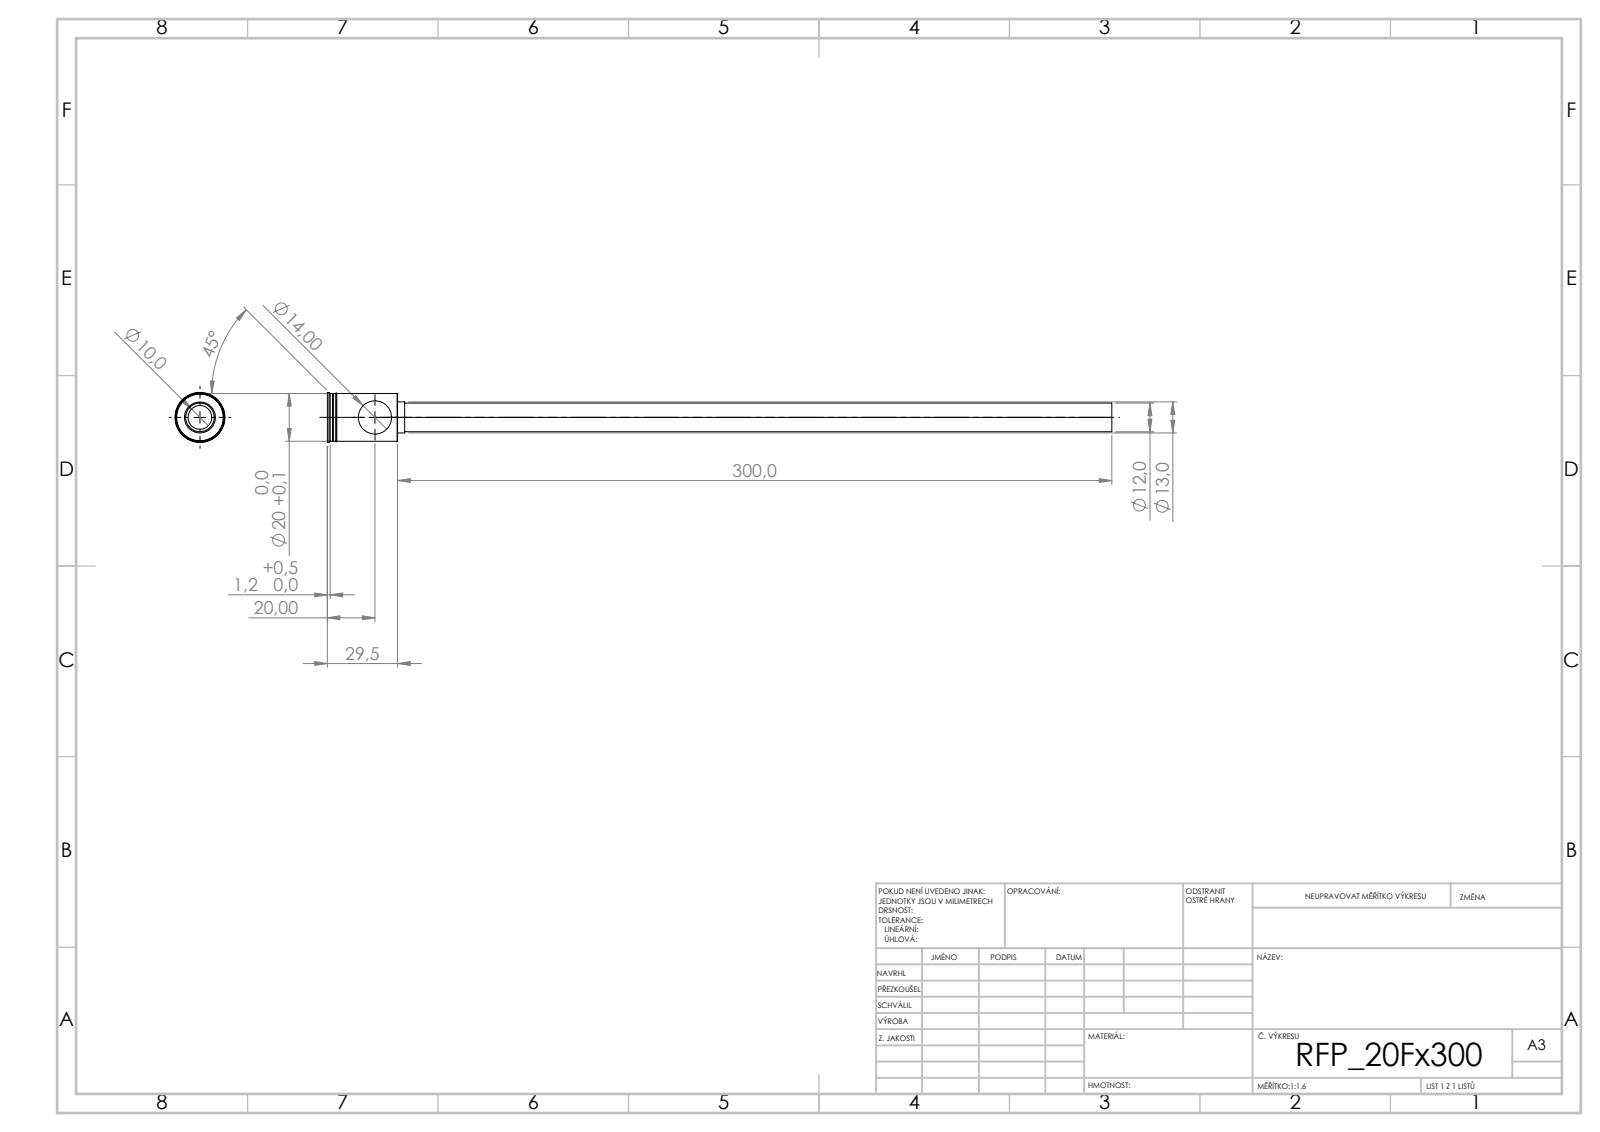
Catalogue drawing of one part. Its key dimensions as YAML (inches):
step_written_by: "SolidWorks 2019 (CONFIG_CONTROL_DESIGN)"
units: inches
bodies: {solids: 1, faces: 44, planar: 20, cylindrical: 16, other: 8}
overall_size: [12.972, 0.827, 0.827]
volume: 0.989
surface_area: 36.88
round_holes:
  - {diameter: 0.394, count: 1}
  - {diameter: 0.551, count: 1}
round_bosses_or_shafts:
  - {diameter: 0.827, count: 1}
  - {diameter: 0.787, count: 1}
  - {diameter: 0.512, count: 1}
  - {diameter: 0.472, count: 1}
face_to_face_distances: [1.083, 0.079, 1.161, 0.606, 11.811, 12.894, 12.972, 0.02, 11.693, 0.118]
